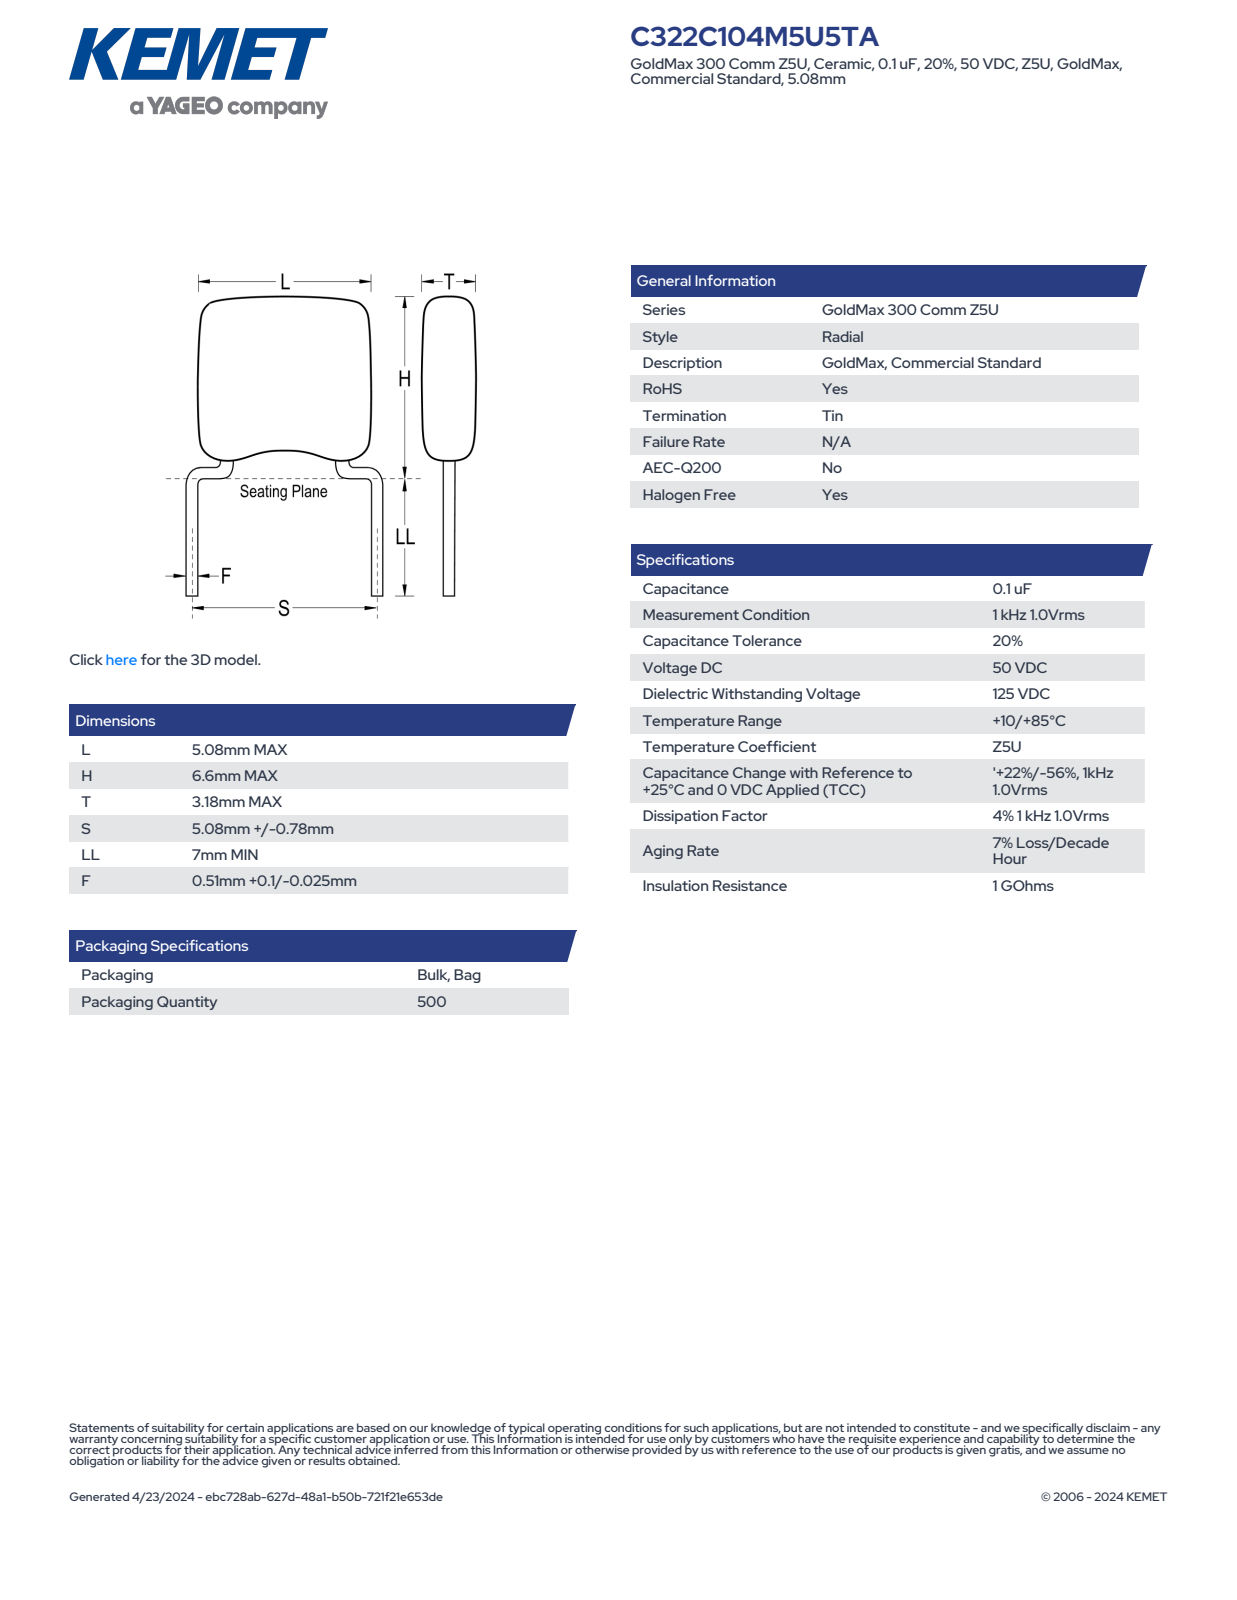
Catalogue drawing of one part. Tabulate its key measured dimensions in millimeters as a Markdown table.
| quantity | value |
| --- | --- |
| part name | CCR_SB_5.08X6.6_L5.08H6.6T3.18S5.08LL7F0.51 |
| STEP written by | SolidWorks 2014 (AUTOMOTIVE_DESIGN) |
| units | millimeters |
| bodies | 4 solids, 97 faces (65 planar, 14 cylindrical, 18 other) |
| overall size | 13.6 × 5.59 × 3.19 |
| volume | 73 mm³ |
| surface area | 123 mm² |
| round bosses / shafts (diameter × count) | 0.51 × 2 |
| partial cylindrical surfaces (radius × count) | 1 × 10 |
| main face-to-face distances | 3.18, 5.08, 4.81, 3.19, 0.43, 2.64, 2.17, 2.21, 2.6, 0.39 |
